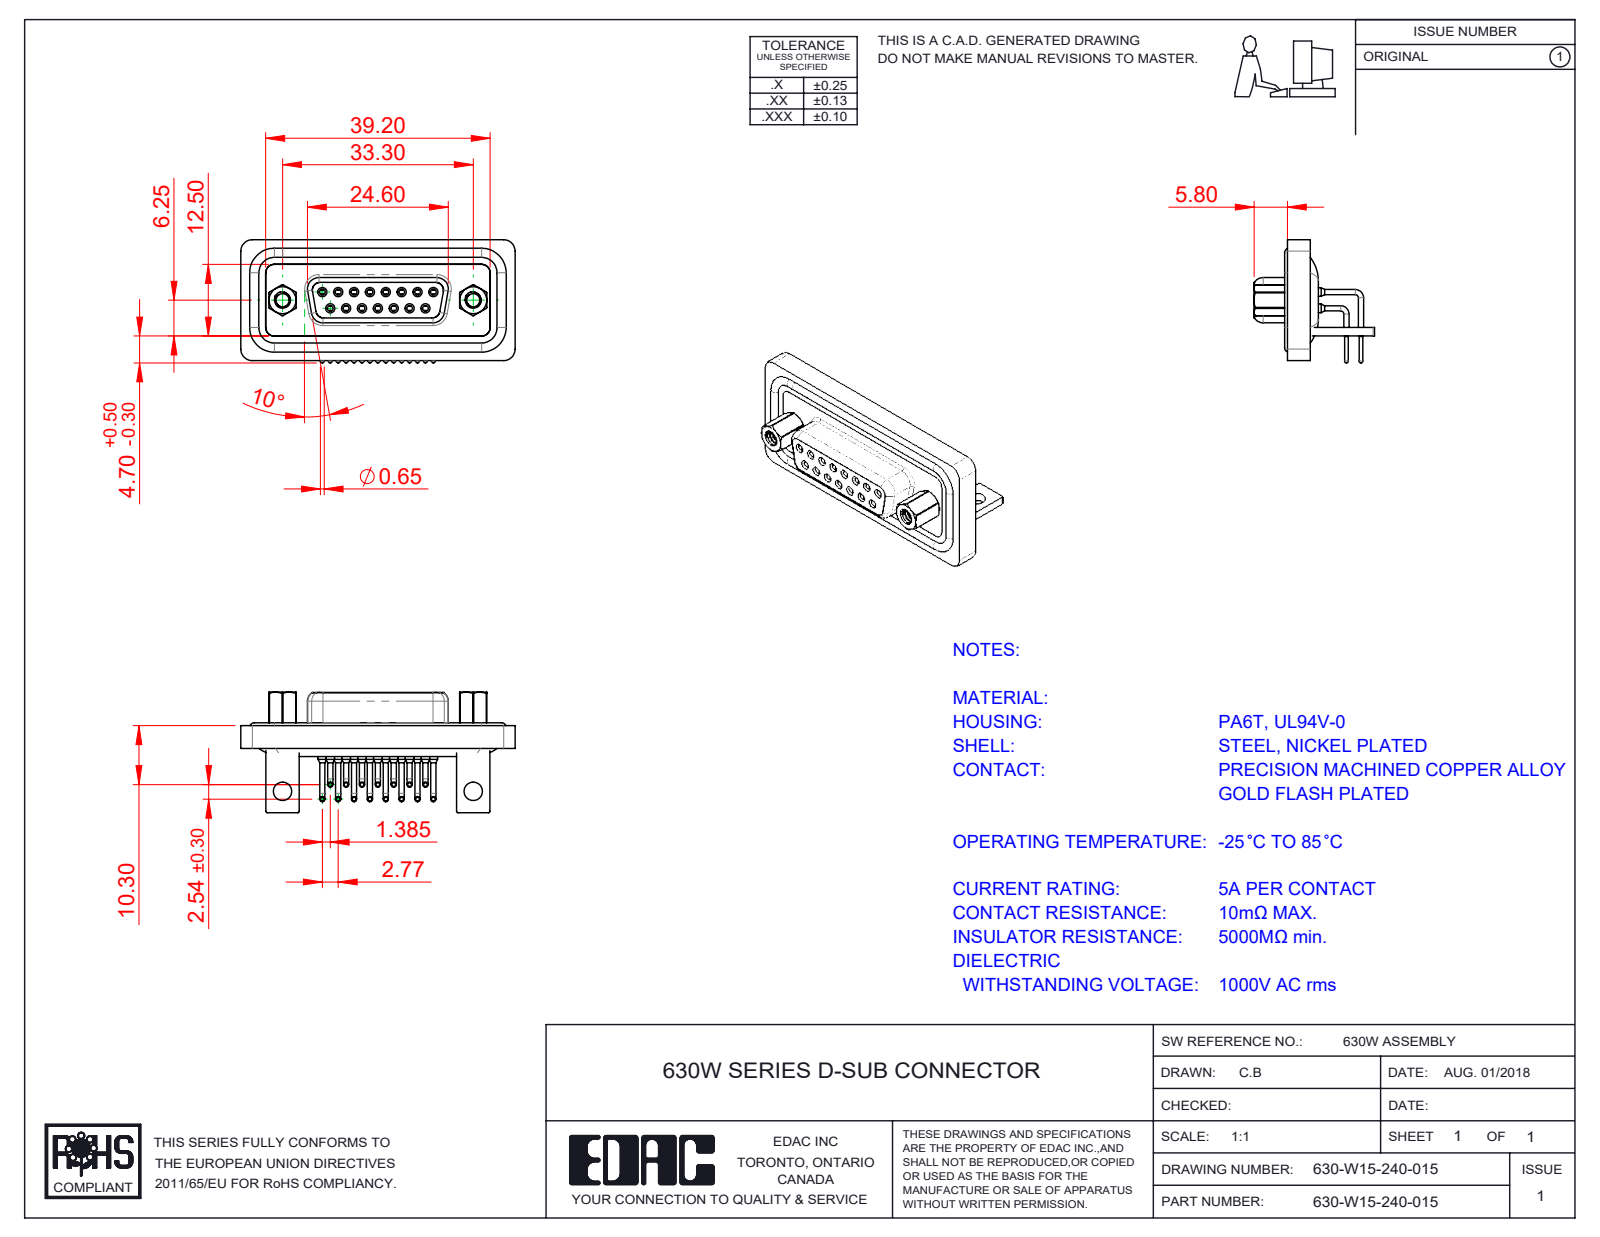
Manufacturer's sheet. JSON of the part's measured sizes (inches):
{"part_name": "630W Stabilizer Bracket; 630W Waterproof Housing_15 Contacts; 630W Contact Row 2; 630W 4-40 Hex Standoff (+5 more)", "step_written_by": "SolidWorks 2016 (CONFIG_CONTROL_DESIGN)", "units": "inches", "bodies": {"solids": 25, "faces": 1294, "planar": 348, "cylindrical": 615, "other": 331}, "overall_size": [1.885, 0.846, 0.829], "volume_in3": 0.359, "surface_area_in2": 16.06, "round_holes": [[0.039, 15], [0.043, 15], [0.059, 15], [0.067, 15], [0.071, 15], [0.079, 15], [0.089, 2], [0.09, 2], [0.126, 2], [0.157, 2], [0.189, 2], [0.193, 2]], "round_bosses_or_shafts": [[0.035, 30], [0.063, 19], [0.059, 15], [0.026, 15], [0.11, 2], [0.197, 1]], "partial_cylinders_radius": [[0.079, 17], [0.059, 14], [0.01, 12], [0.053, 8], [0.106, 6], [0.02, 5], [0.035, 4], [0.063, 4]], "face_to_face_distances": [0.016, 0.071, 0.063, 0.043, 0.098, 0.114, 0.169, 0.386, 0.228, 0.02], "hole_center_spacings": [0.124, 0.109, 0.218, 0.327, 0.125, 0.124, 0.436, 0.198]}
